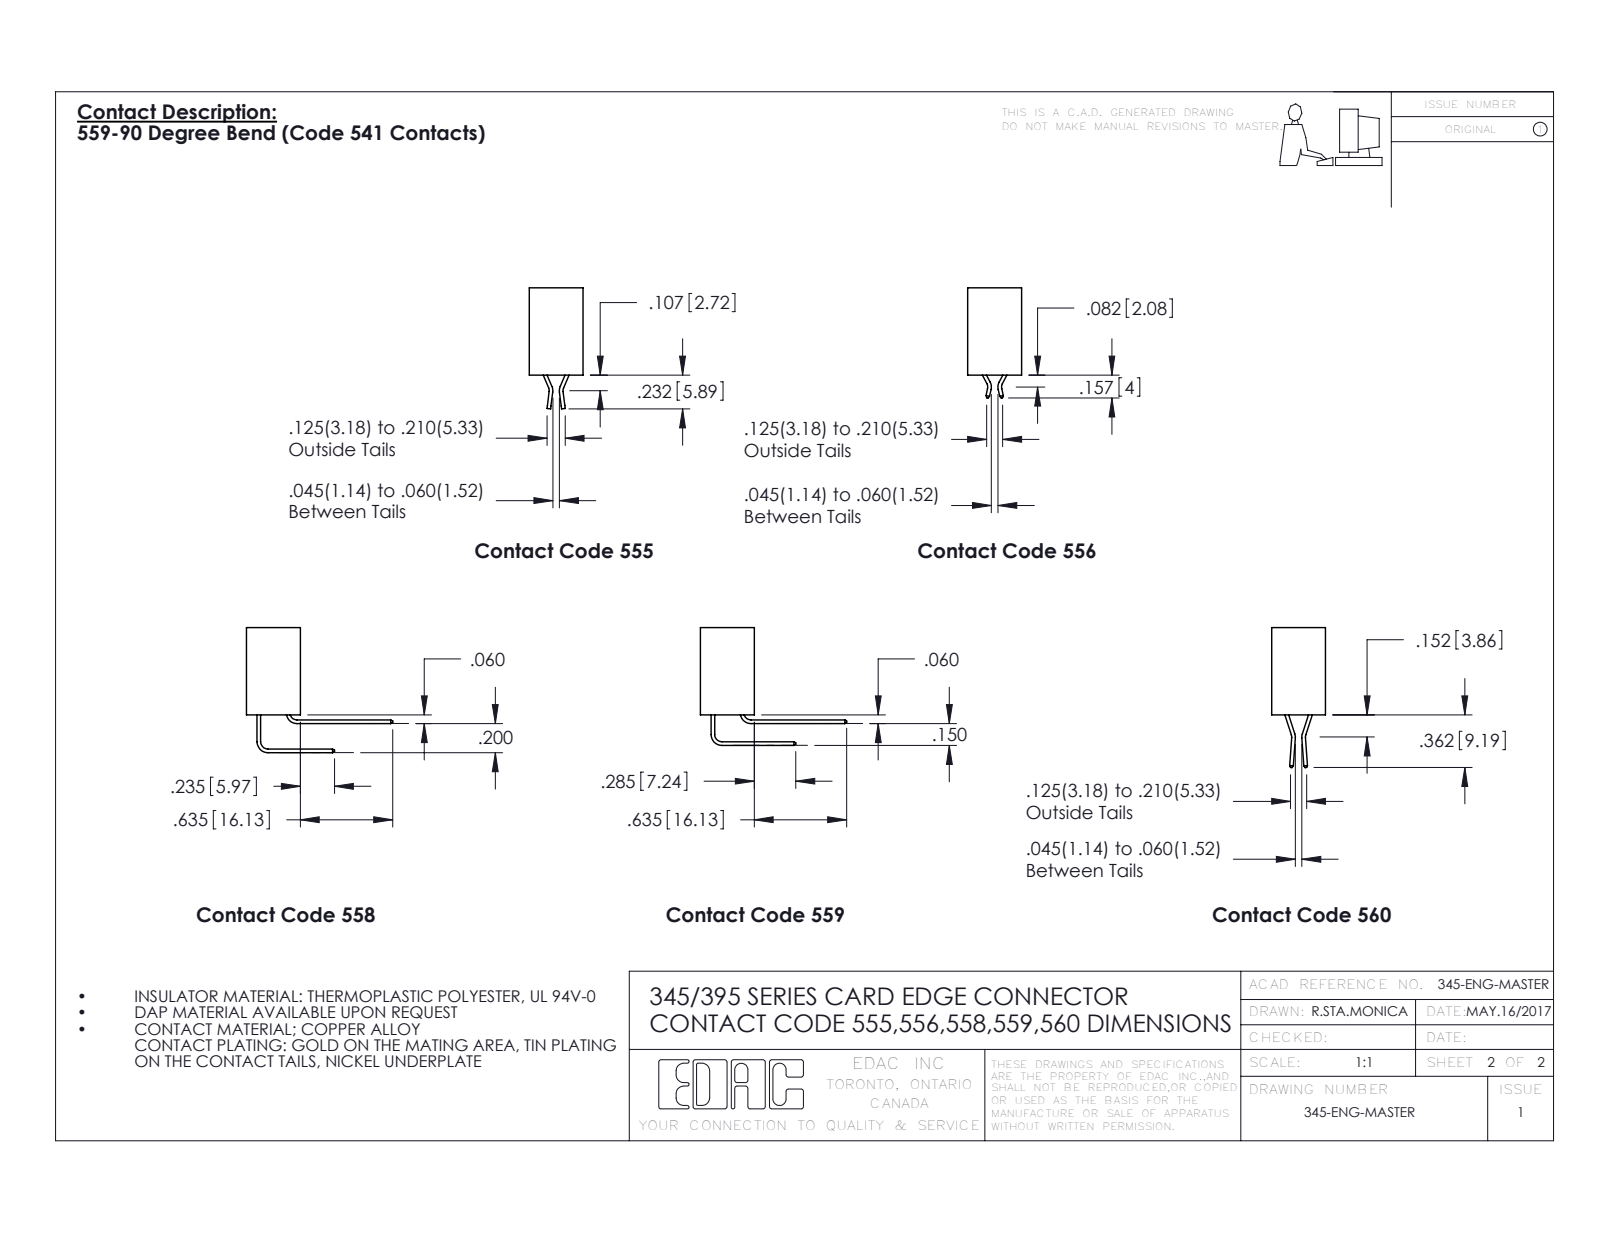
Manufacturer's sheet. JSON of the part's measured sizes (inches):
{"part_name": "345 Part_0.110 Offset - Side Mount; 395-128-555-512; 345-292-001_555 Tail", "step_written_by": "SolidWorks 2016 (CONFIG_CONTROL_DESIGN)", "units": "inches", "bodies": {"solids": 129, "faces": 7298, "planar": 4052, "cylindrical": 3246, "other": 0}, "overall_size": [7.235, 0.832, 0.37], "volume_in3": 1.115, "surface_area_in2": 44.45, "round_holes": [[0.128, 2], [0.064, 1]], "partial_cylinders_radius": [[0.016, 320], [0.02, 256], [0.006, 192], [0.01, 22], [0.007, 6], [0.031, 6], [0.026, 3], [0.01, 2]], "face_to_face_distances": [0.298, 0.072, 0.025, 0.37, 0.2, 0.098, 0.272, 0.225, 0.175, 0.149], "hole_center_spacings": [6.975]}
